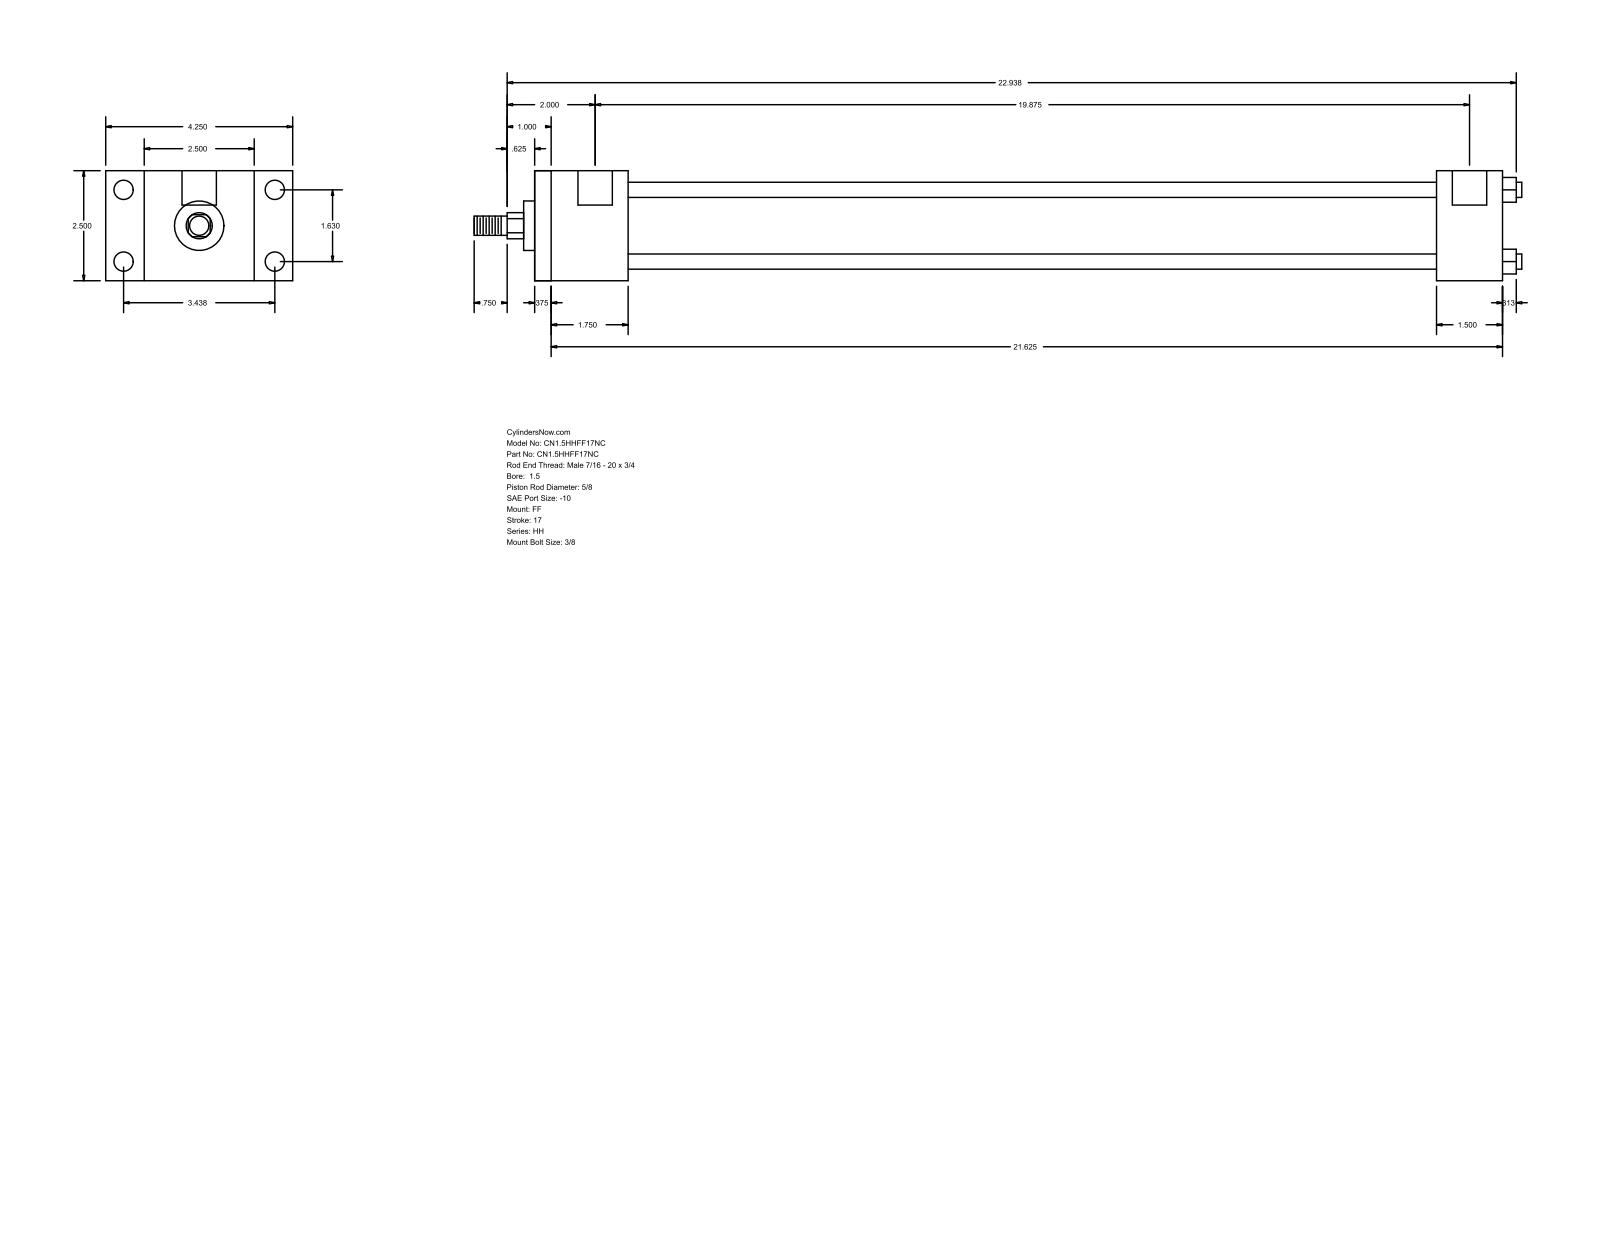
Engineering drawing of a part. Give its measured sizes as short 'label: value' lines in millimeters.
name: HH_FF__0150_0.625
written by: GSSL Pune (CONFIG_CONTROL_DESIGN)
unit: mm
bodies: 0 solids, 92 faces (64 planar, 28 cylindrical, 0 other)
size: 604.84 × 107.95 × 63.5
holes: 4× ⌀5.56, 4× ⌀11.13, 2× ⌀19.84
bosses: 4× ⌀8.76, 1× ⌀44.45, 1× ⌀28.57, 1× ⌀15.88, 1× ⌀11.11
rounds: 1× R7.54
face distances: 63.5, 558.79, 9.52, 549.27, 44.45, 53.97, 504.82, 520.7, 511.18, 466.73
hole spacings: 1.59, 41.4, 87.32, 96.64, 506.41, 508, 504.82
